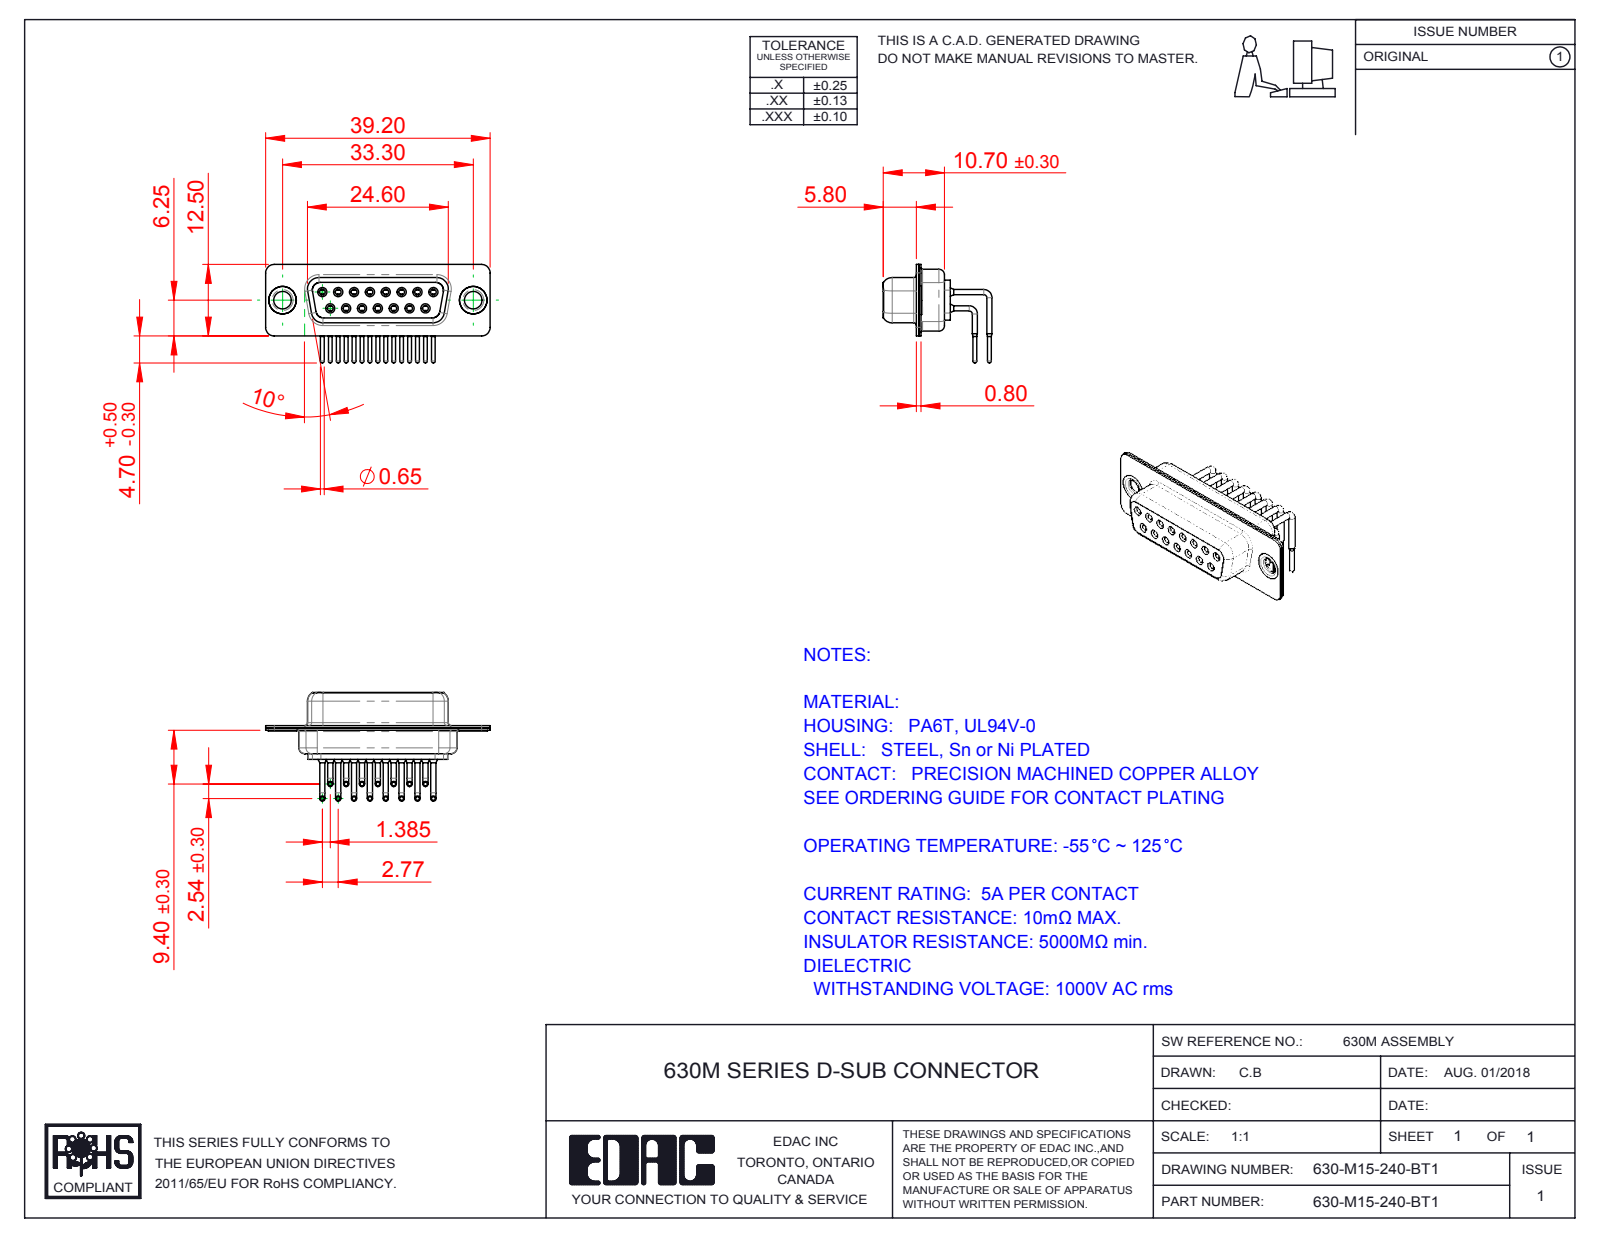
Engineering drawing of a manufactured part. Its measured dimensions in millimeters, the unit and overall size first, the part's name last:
Units: millimetres
Overall size (bounding box): 39.2 × 18.99 × 17.2
Round holes (diameter × count): ⌀1 ×15, ⌀1.1 ×15, ⌀1.7 ×15, ⌀1.8 ×15, ⌀2 ×15, ⌀3.05 ×2, ⌀4 ×2, ⌀4.8 ×2
Round bosses / shafts (diameter × count): ⌀0.9 ×30, ⌀1.6 ×15, ⌀1.5 ×15, ⌀0.65 ×15, ⌀5 ×2, ⌀4.9 ×2, ⌀3.55 ×2
Partial cylindrical surfaces — rounded edges, fillets, slot ends (radius × count): R1.5 ×16, R2 ×12, R1.35 ×8, R1.6 ×8, R0.25 ×4, R0.5 ×4, R0.6 ×4, R0.65 ×4
Main face-to-face distances: 0.4, 1.45, 8.95, 6.2, 1.9, 8.5, 2.3, 0.45, 7.05, 0.85
Hole centre spacings: 3.16, 2.77, 5.54, 8.31, 11.08, 5.03, 5.04, 7.48
Volume: 2 488 mm³ · Surface area: 6 404 mm²
Bodies: 20 solids, 1048 faces (292 planar, 466 cylindrical, 290 other)
Part name (STEP PRODUCT): 630M Shell Front_15 Contacts; 630M Housing_15 Contacts; 630M Shell Rear_15 Contacts; 630M Thru Hole Rivet (+3 more)
STEP written by: SolidWorks 2016 (CONFIG_CONTROL_DESIGN)
